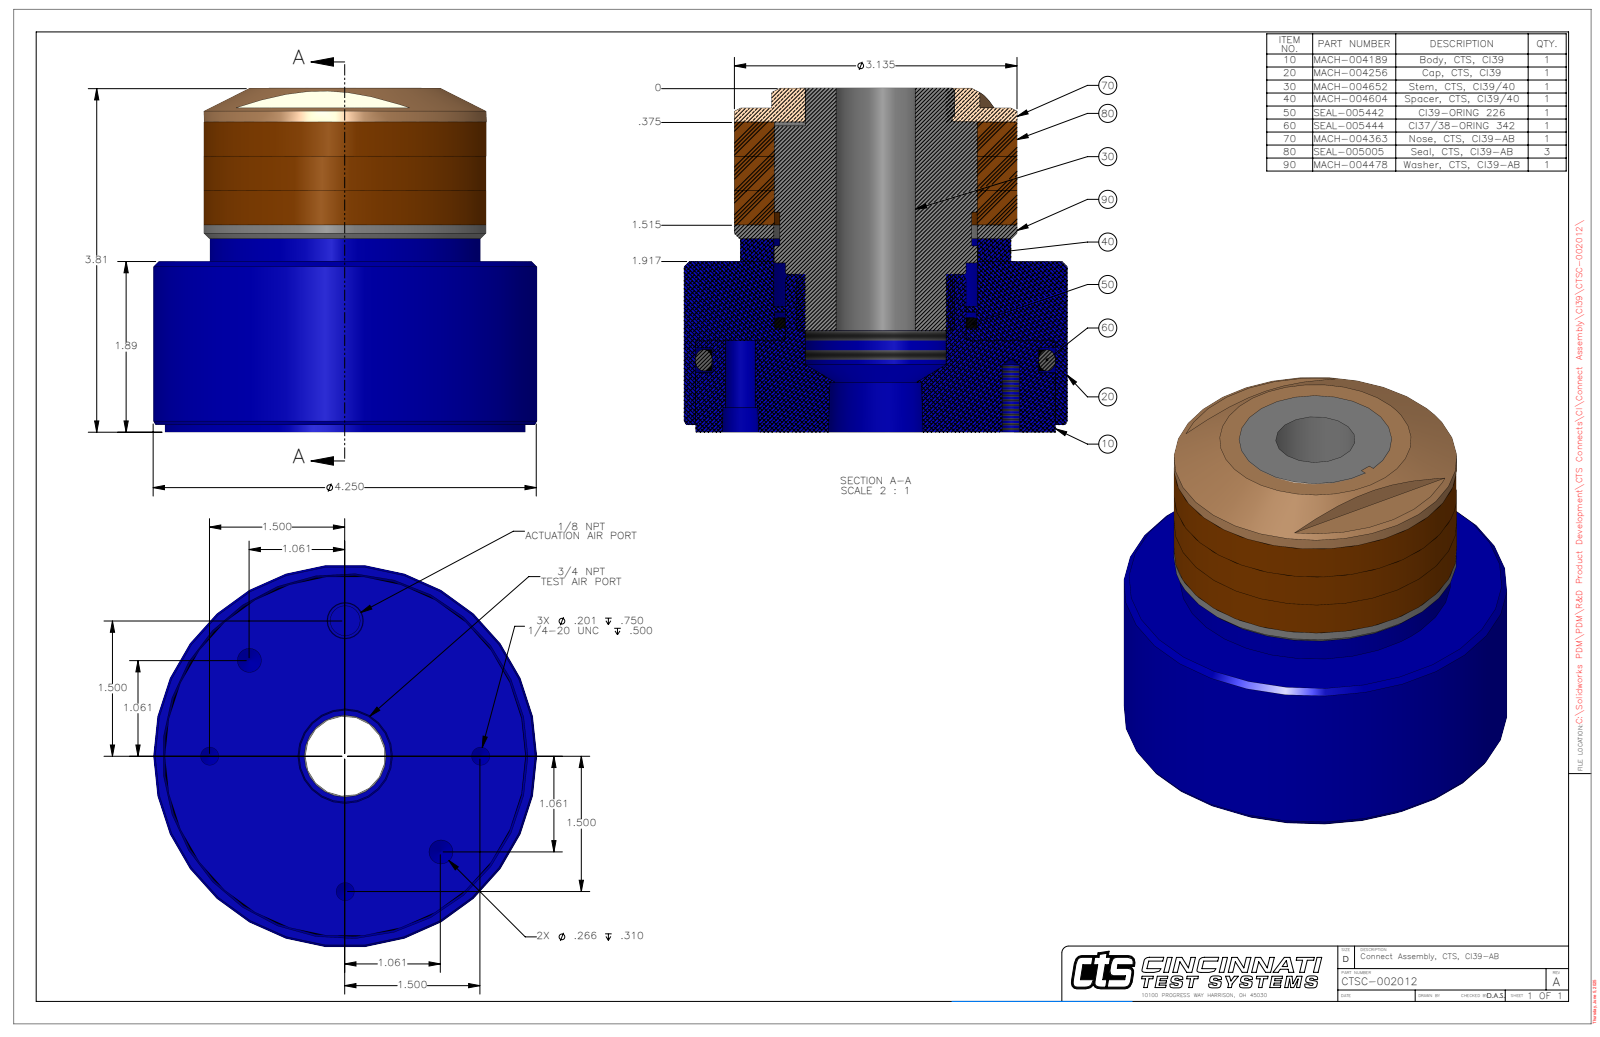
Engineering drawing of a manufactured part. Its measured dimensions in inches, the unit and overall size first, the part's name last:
Units: inches
Overall size (bounding box): 4.25 × 4.25 × 3.813
Round holes (diameter × count): ⌀0.201 ×3, ⌀0.266 ×2, ⌀0.332 ×1, ⌀0.88 ×1, ⌀2.25 ×1, ⌀2.26 ×1, ⌀2.261 ×1, ⌀4 ×1
Round bosses / shafts (diameter × count): ⌀4.25 ×1, ⌀3.992 ×1, ⌀3.135 ×1, ⌀3 ×1, ⌀2.12 ×1
Partial cylindrical surfaces — rounded edges, fillets, slot ends (radius × count): R0.062 ×1, R0.781 ×1
Main face-to-face distances: 1.893, 3.813, 1.92, 3.81, 1.917, 0.083, 1.81, 3.727, 3.73, 3.591
Hole centre spacings: 1.5, 1.148, 2.121, 2.772, 3
Volume: 38 in³ · Surface area: 101.9 in²
Bodies: 1 solid, 94 faces (32 planar, 39 cylindrical, 23 other)
Part name (STEP PRODUCT): CTSC-002012
STEP written by: SolidWorks 2023 (AUTOMOTIVE_DESIGN)
